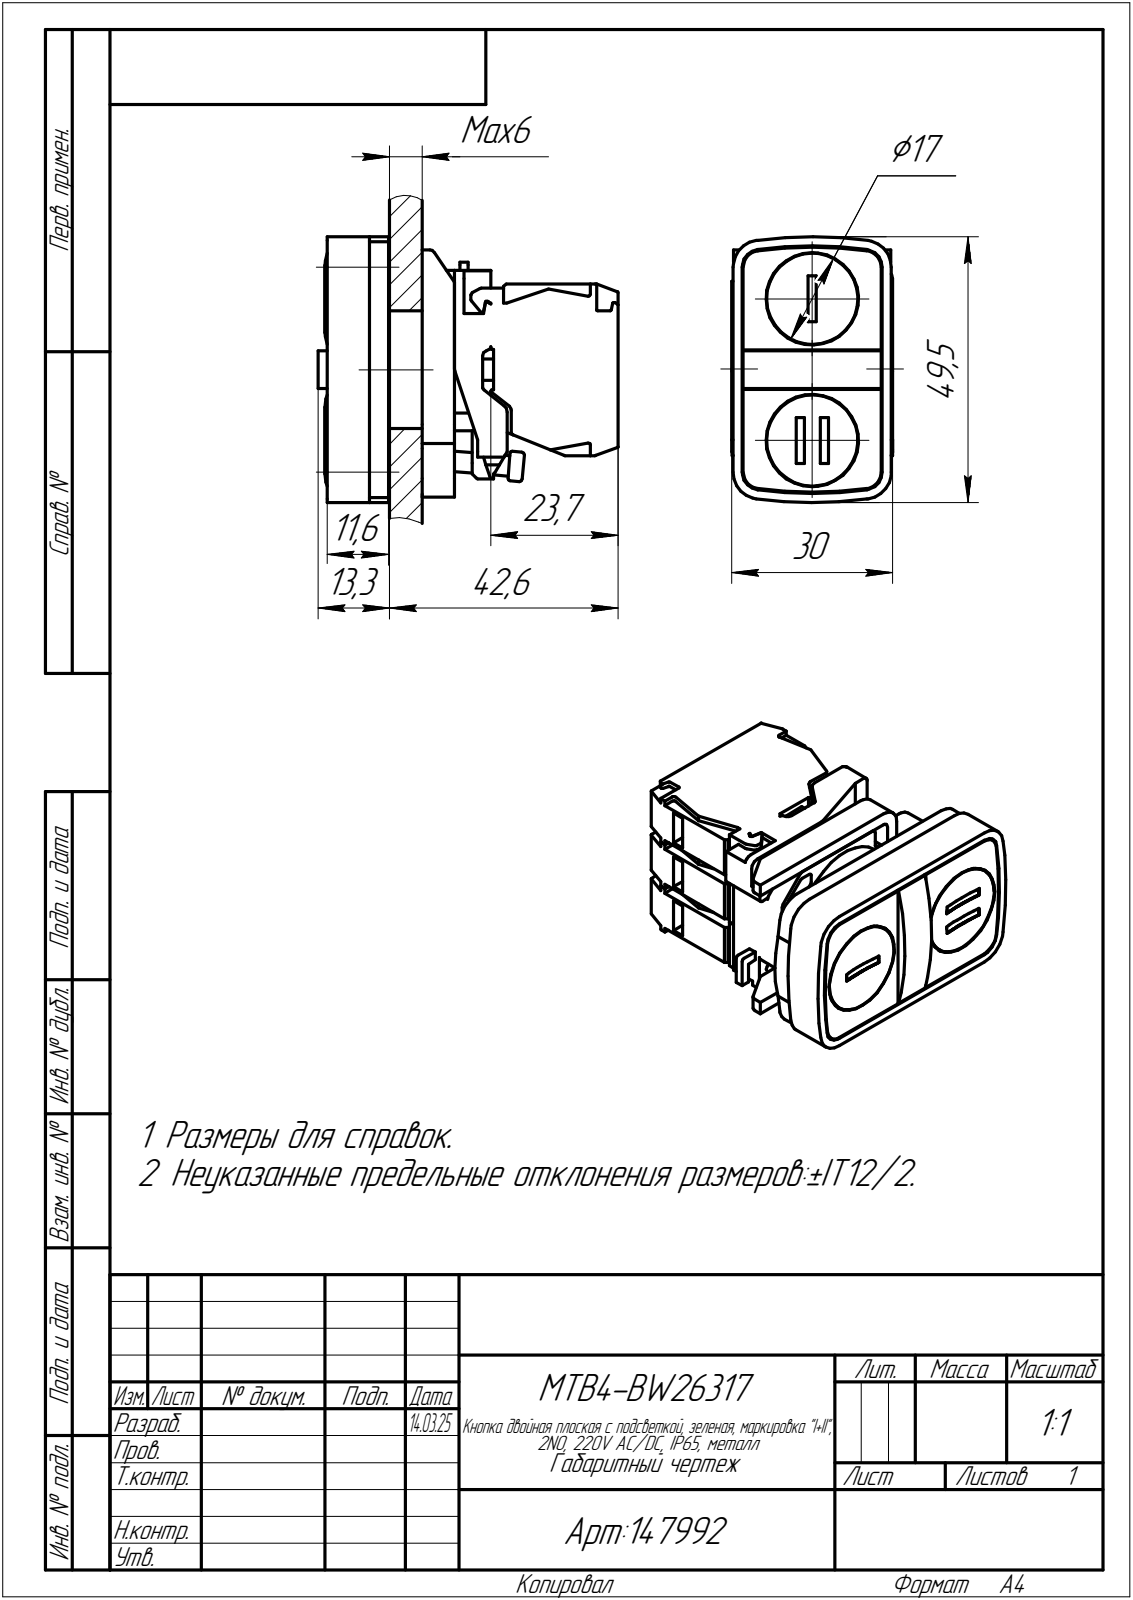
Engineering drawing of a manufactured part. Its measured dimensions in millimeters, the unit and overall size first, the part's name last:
Units: millimetres
Overall size (bounding box): 55.9 × 49.5 × 30
Round holes (diameter × count): ⌀1.5 ×2, ⌀6 ×2, ⌀17.2 ×2, ⌀20.5 ×1
Round bosses / shafts (diameter × count): ⌀17 ×2, ⌀26.8 ×1, ⌀22 ×1, ⌀5.5 ×1, ⌀3.8 ×1
Partial cylindrical surfaces — rounded edges, fillets, slot ends (radius × count): R0.5 ×23, R0.2 ×10, R0.8 ×7, R1 ×5, R1.02 ×4, R3.1 ×4, R3.3 ×4, R3.52 ×4
Main face-to-face distances: 10, 9.9, 20, 19.9, 10.1, 11.4, 2.5, 29.9, 1.82, 9.75
Hole centre spacings: 4.7, 8.5, 13.2, 21.7, 11.56, 11.88, 12.63, 13.77
Volume: 48 405 mm³ · Surface area: 20 801 mm²
Bodies: 2 solids, 628 faces (424 planar, 180 cylindrical, 24 other)
Part name (STEP PRODUCT): MTB4-BW26317
STEP written by: C3D Toolkit (CONFIG_CONTROL_DESIGN)
